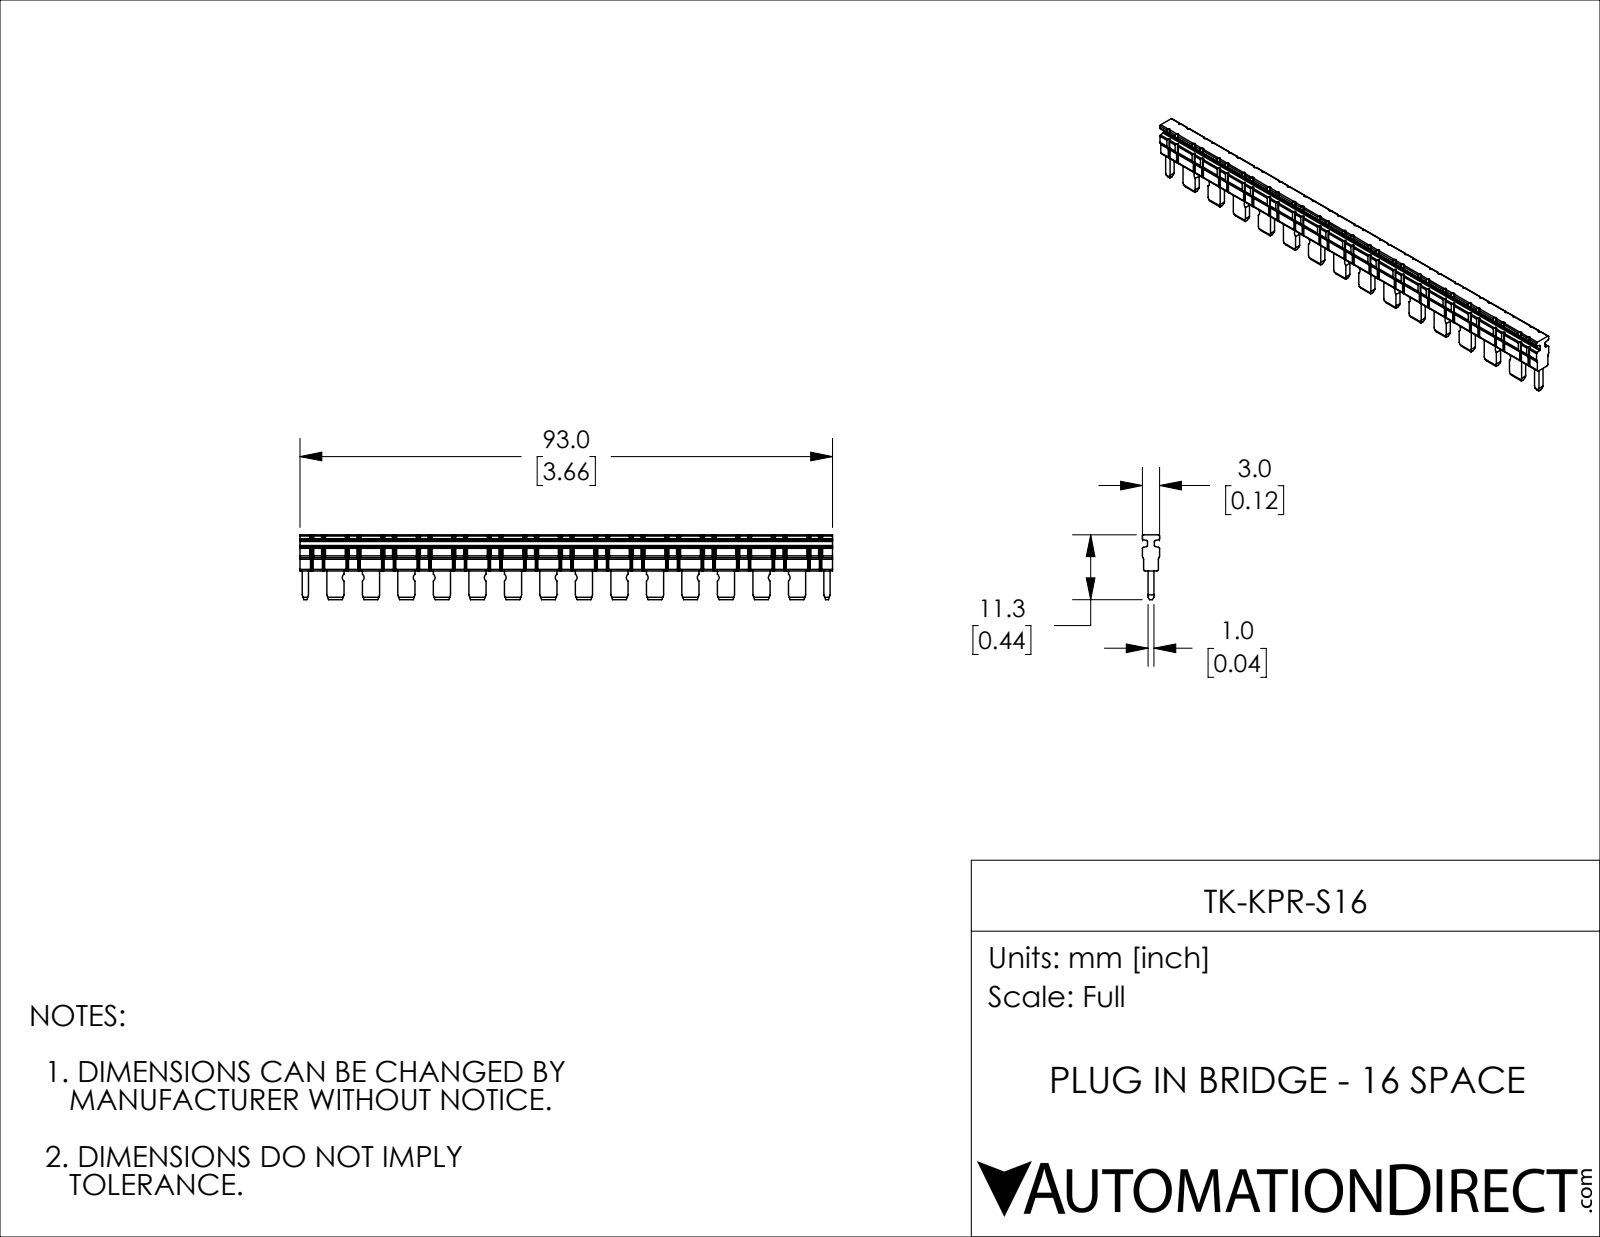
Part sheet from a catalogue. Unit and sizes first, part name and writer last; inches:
Units: inches
Overall size (bounding box): 3.661 × 0.445 × 0.118
Partial cylindrical surfaces — rounded edges, fillets, slot ends (radius × count): R0.006 ×60, R0.012 ×32, R0.03 ×14, R0.008 ×10, R0.02 ×4
Main face-to-face distances: 0.039, 0.11, 0.031, 0.071, 0.079, 0.118, 0.138, 0.248, 0.102, 0.043
Volume: 0.1 in³ · Surface area: 6.298 in²
Bodies: 2 solids, 1140 faces (630 planar, 510 cylindrical, 0 other)
Part name (STEP PRODUCT): TK-KPR-S16
STEP written by: SolidWorks 2018 (AUTOMOTIVE_DESIGN)
